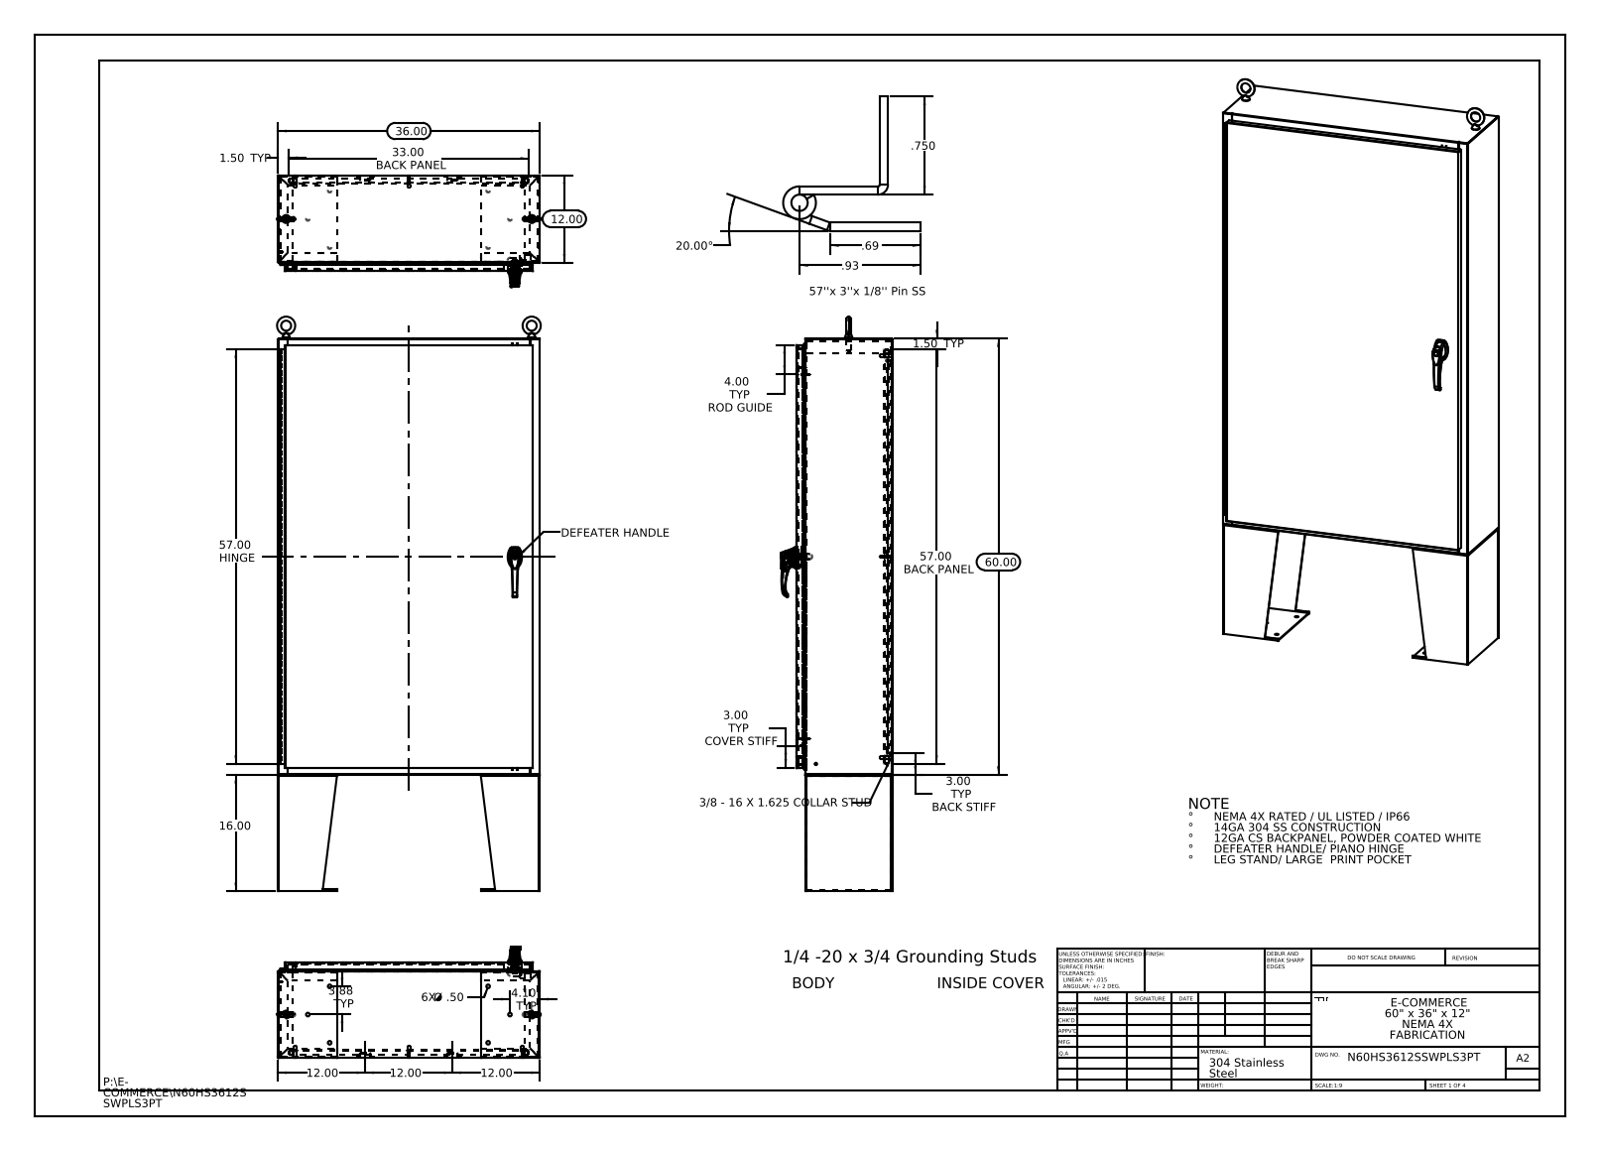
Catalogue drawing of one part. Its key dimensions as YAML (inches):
part_name: "00005090; 00005310_26163101; 21130102; N60HS3612SSWPLS3PT Body (+8 more)"
step_written_by: "SolidWorks 2013 (CONFIG_CONTROL_DESIGN)"
units: inches
bodies: {solids: 55, faces: 3808, planar: 1529, cylindrical: 1461, other: 818}
overall_size: [79, 36.271, 15.307]
volume: 924
surface_area: 22182
round_holes:
  - {diameter: 0.5, count: 14}
  - {diameter: 0.25, count: 10}
  - {diameter: 0.75, count: 4}
  - {diameter: 0.138, count: 3}
  - {diameter: 0.161, count: 3}
  - {diameter: 0.079, count: 2}
  - {diameter: 0.203, count: 2}
  - {diameter: 0.313, count: 2}
  - {diameter: 0.437, count: 2}
  - {diameter: 0.125, count: 1}
  - {diameter: 0.125, count: 1}
  - {diameter: 0.197, count: 1}
round_bosses_or_shafts:
  - {diameter: 0.625, count: 10}
  - {diameter: 0.157, count: 10}
  - {diameter: 0.14, count: 10}
  - {diameter: 0.375, count: 8}
  - {diameter: 0.33, count: 8}
  - {diameter: 0.315, count: 3}
  - {diameter: 0.236, count: 3}
  - {diameter: 1.181, count: 1}
partial_cylinders:
  - {radius: 0.118, count: 37}
  - {radius: 0.013, count: 34}
  - {radius: 0.006, count: 33}
  - {radius: 0.088, count: 28}
  - {radius: 0.039, count: 15}
  - {radius: 0.028, count: 12}
  - {radius: 0.039, count: 8}
  - {radius: 0.143, count: 8}
face_to_face_distances: [0.075, 13.126, 0.104, 13.051, 1.075, 13.201, 1, 12.051, 12.126, 1.179]
hole_center_spacings: [7.137, 13.578, 23.354, 25.094, 25.662, 27.625, 41.709, 52.467]
